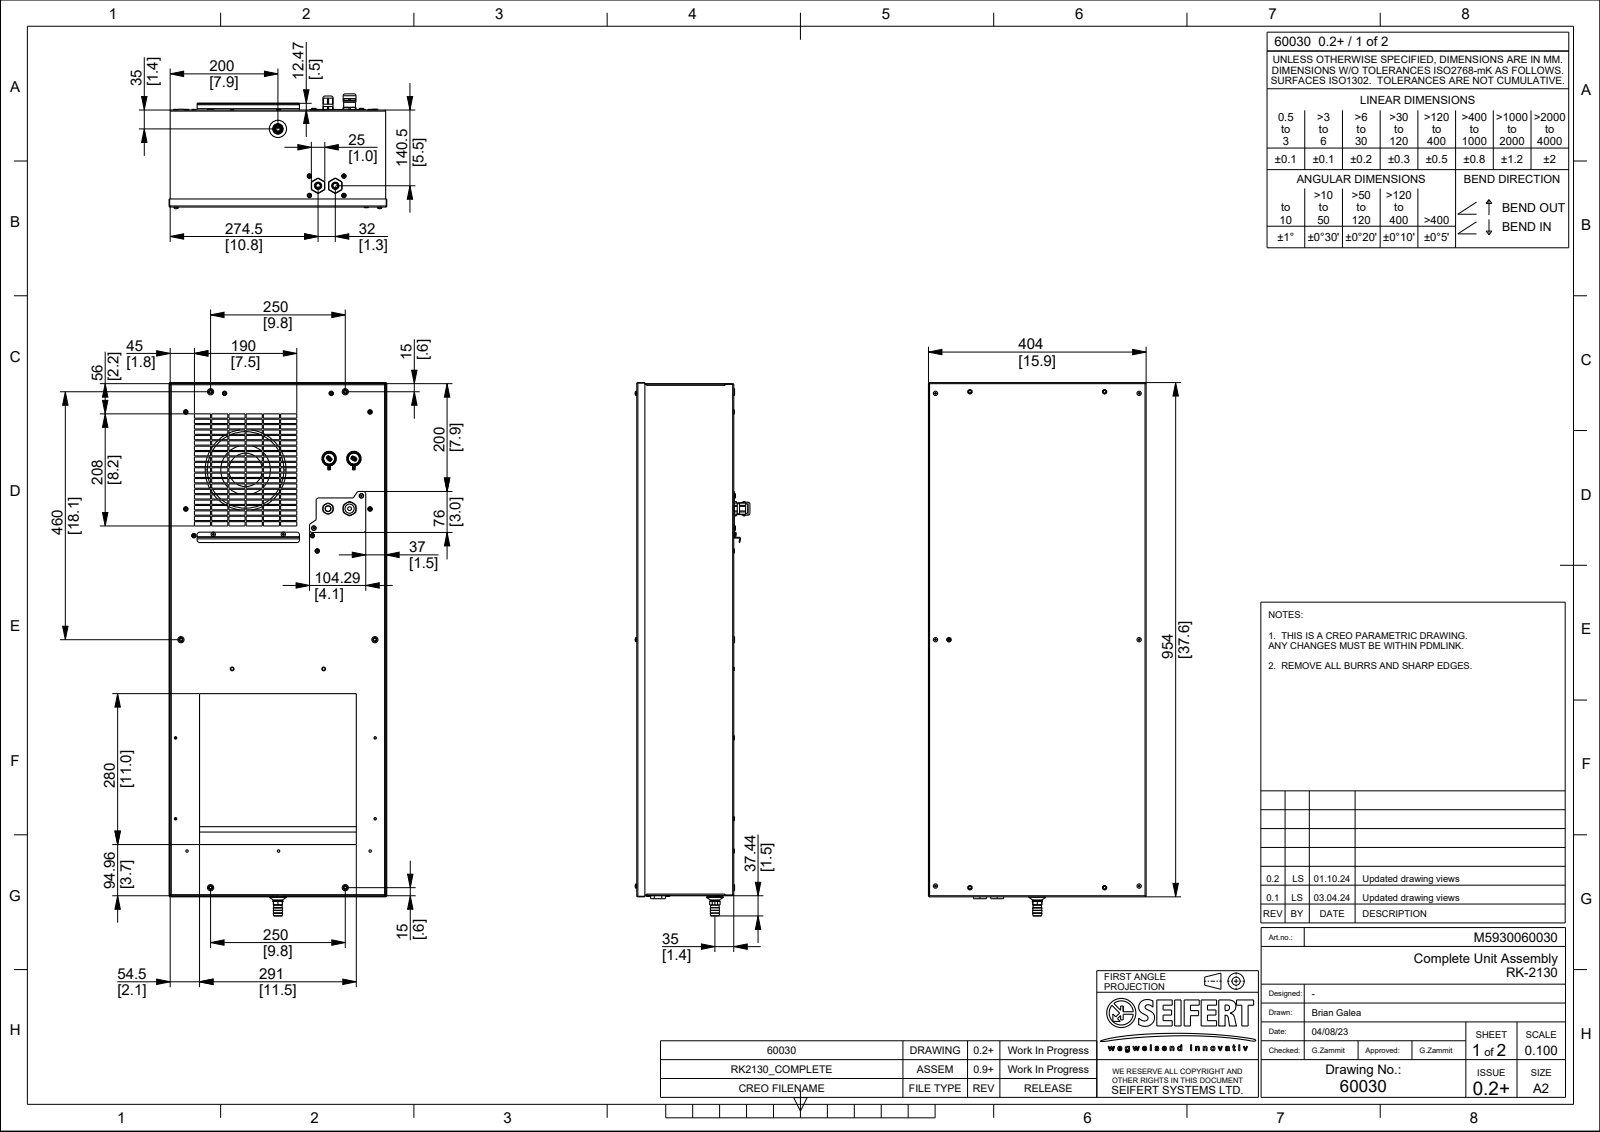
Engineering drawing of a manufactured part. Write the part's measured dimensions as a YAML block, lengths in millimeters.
part_name: "60030"
step_written_by: "CREO PARAMETRIC BY PTC INC, 2023294 (CONFIG_CONTROL_DESIGN)"
units: millimeters
bodies: {solids: 13, faces: 5832, planar: 3087, cylindrical: 1051, other: 1694}
overall_size: [1004.19, 404, 211.25]
volume: 1285000
surface_area: 2591000
round_holes:
  - {diameter: 4.5, count: 23}
  - {diameter: 7, count: 17}
  - {diameter: 6, count: 16}
  - {diameter: 4, count: 6}
  - {diameter: 5, count: 6}
  - {diameter: 5.5, count: 6}
  - {diameter: 0.8, count: 5}
  - {diameter: 3, count: 4}
  - {diameter: 8, count: 4}
  - {diameter: 2.9, count: 2}
  - {diameter: 3.9, count: 2}
  - {diameter: 9, count: 2}
round_bosses_or_shafts:
  - {diameter: 11.5, count: 6}
  - {diameter: 9, count: 6}
  - {diameter: 24.2, count: 3}
  - {diameter: 17.5, count: 2}
  - {diameter: 16.6, count: 2}
  - {diameter: 14.7, count: 2}
  - {diameter: 8.28, count: 2}
  - {diameter: 4, count: 2}
partial_cylinders:
  - {radius: 0.5, count: 87}
  - {radius: 0.3, count: 68}
  - {radius: 2.5, count: 36}
  - {radius: 1, count: 28}
  - {radius: 1.38, count: 24}
  - {radius: 1.5, count: 19}
  - {radius: 2, count: 18}
  - {radius: 4.73, count: 16}
face_to_face_distances: [1, 179, 399, 178, 180, 400, 2, 398, 949, 177]
hole_center_spacings: [0.84, 24.08, 51.26, 64.07, 314.01, 457, 464.43, 556.95]
